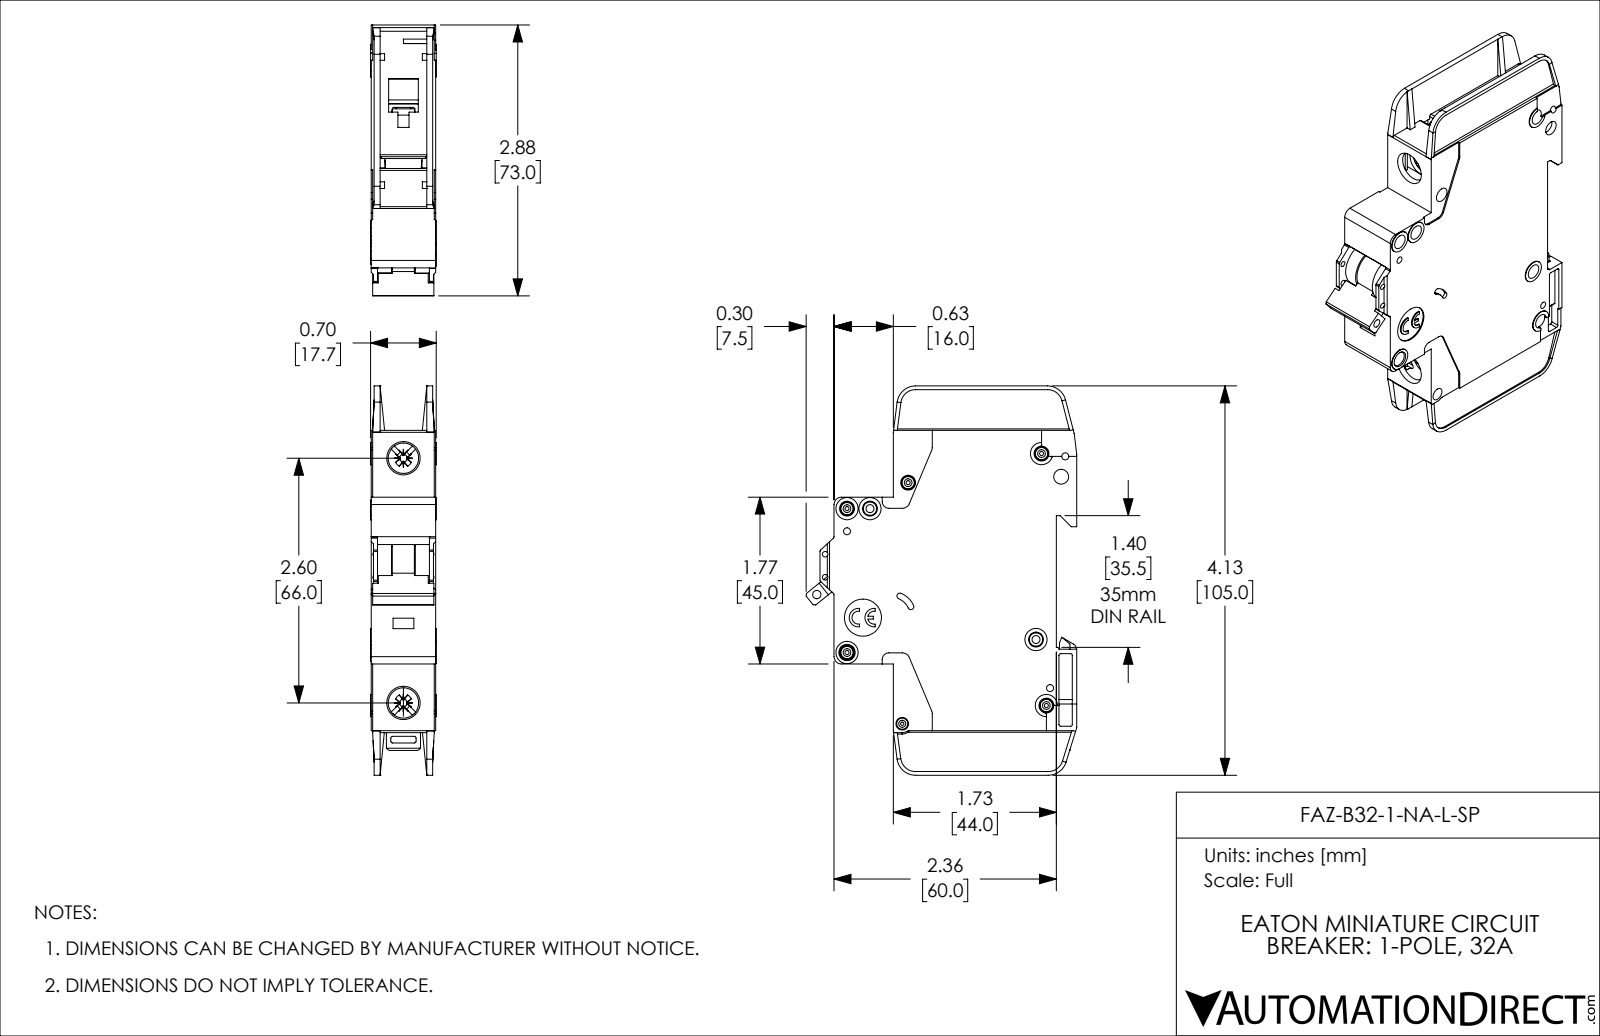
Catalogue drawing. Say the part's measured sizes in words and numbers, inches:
The part is named "FAZ-B32-1-NA-L-SP". Its 3-D file was written by "SolidWorks 2019 (AUTOMOTIVE_DESIGN)". It is 1 solid with 1127 faces: 671 planar, 357 cylindrical and 99 other. Overall it measures 4.134 by 2.876 by 0.697 inches. Its volume is 4.682 cubic inches and its surface area 41.01 square inches. Round holes: 8 of diameter 0.157, 5 of diameter 0.043, 4 of diameter 0.075, 2 of diameter 0.059, 2 of diameter 0.085, 2 of diameter 0.323, 1 of diameter 0.035, 1 of diameter 0.089, 1 of diameter 0.098, 1 of diameter 0.134, 1 of diameter 0.394. Round bosses or shafts: 5 of diameter 0.13, 4 of diameter 0.236, 2 of diameter 0.118, 1 of diameter 0.098. Partial cylindrical surfaces (rounded edges, fillets, slot ends): 42 of radius 0.02, 10 of radius 0.016, 10 of radius 0.039, 8 of radius 0.079, 5 of radius 0.197, 4 of radius 0.008, 4 of radius 0.026, 4 of radius 0.043. The main face-to-face distances are 0.047, 0.685, 0.591, 0.638, 0.094, 0.543, 0.016, 0.031, 0.496, 0.575. The hole center spacings are 0.244, 0.537, 0.87, 0.189, 0.199, 0.204, 0.221, 0.24.
